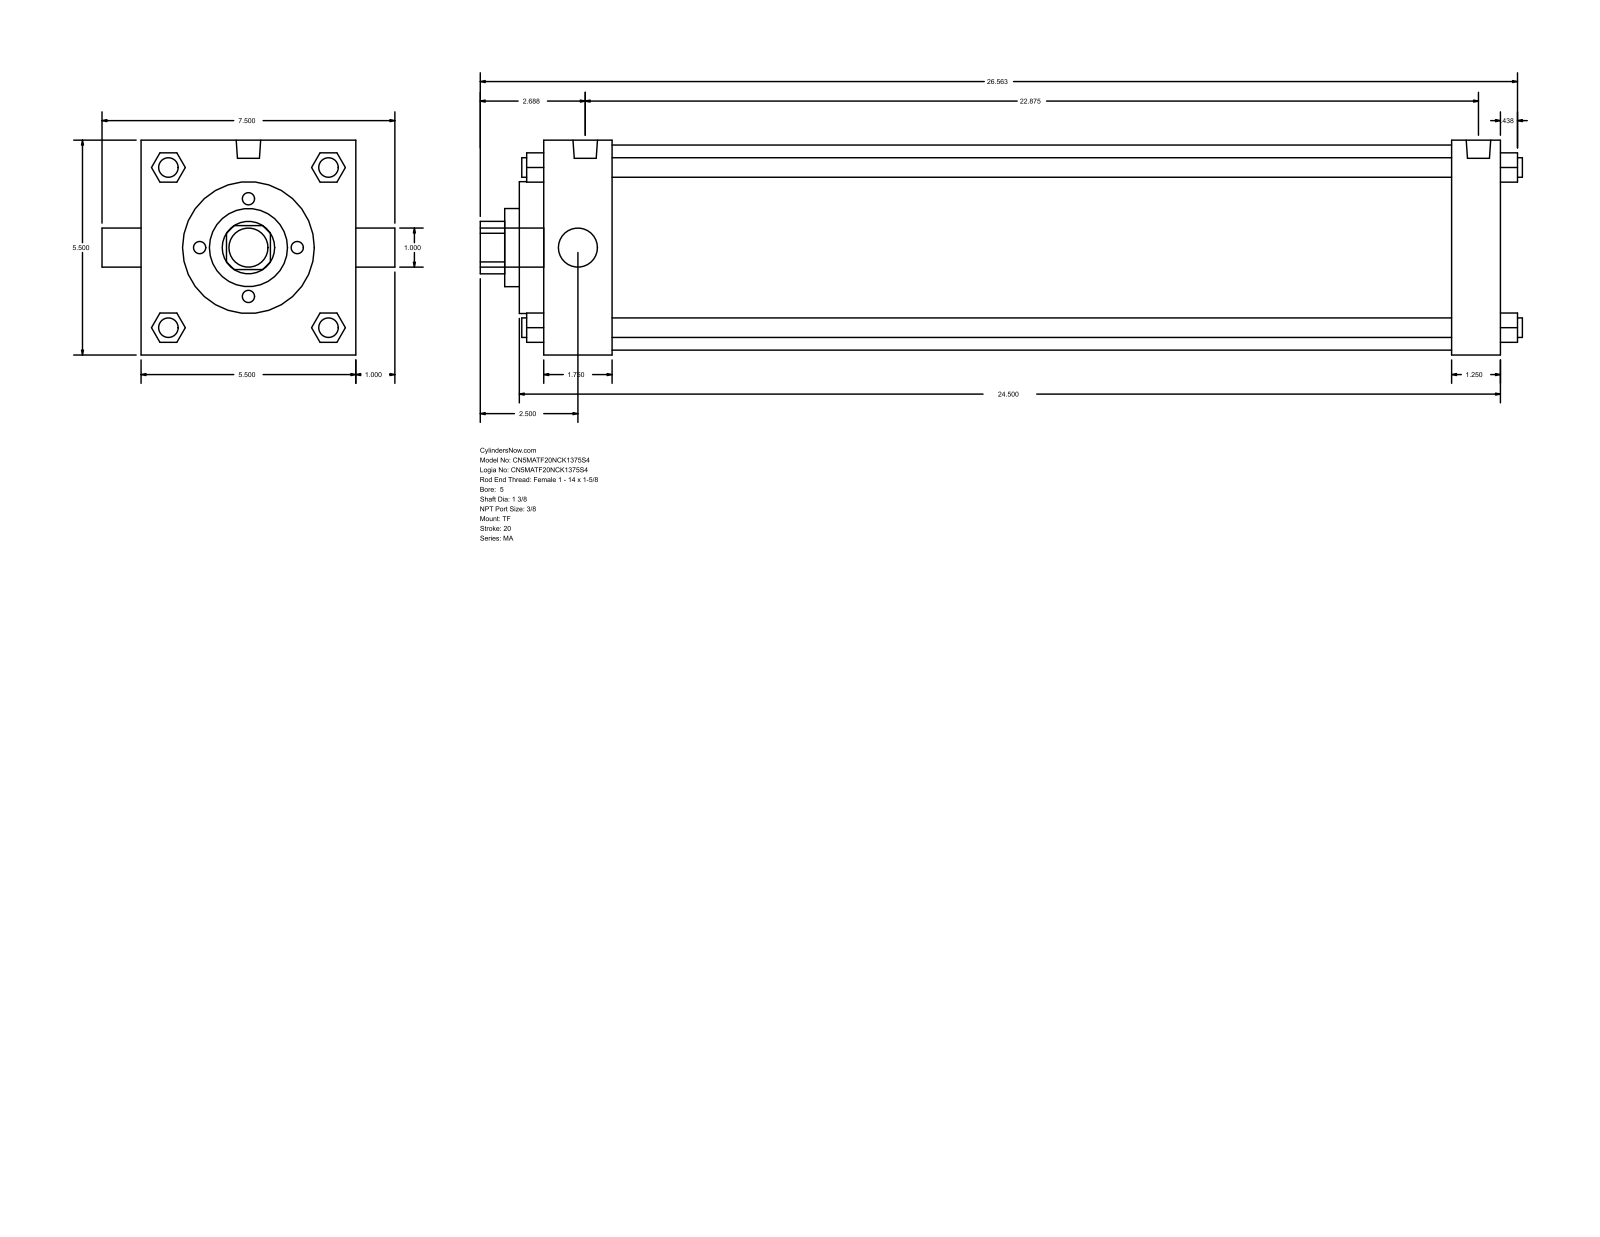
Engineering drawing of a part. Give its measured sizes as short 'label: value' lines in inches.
name: MA_TF__0500_1.375
written by: GSSL Pune (CONFIG_CONTROL_DESIGN)
unit: in
bodies: 0 solids, 122 faces (93 planar, 29 cylindrical, 0 other)
size: 26.687 × 7.5 × 5.5
holes: 1× ⌀1, 1× ⌀1.375, 1× ⌀2, 1× ⌀3.375, 1× ⌀5.25
bosses: 4× ⌀0.5, 3× ⌀0.437, 2× ⌀0.627, 1× ⌀1
rounds: 1× R0.672
face distances: 5.5, 24.5, 23.25, 1.25, 1.75, 21.5, 22.75, 0.625, 2.375, 23.875
